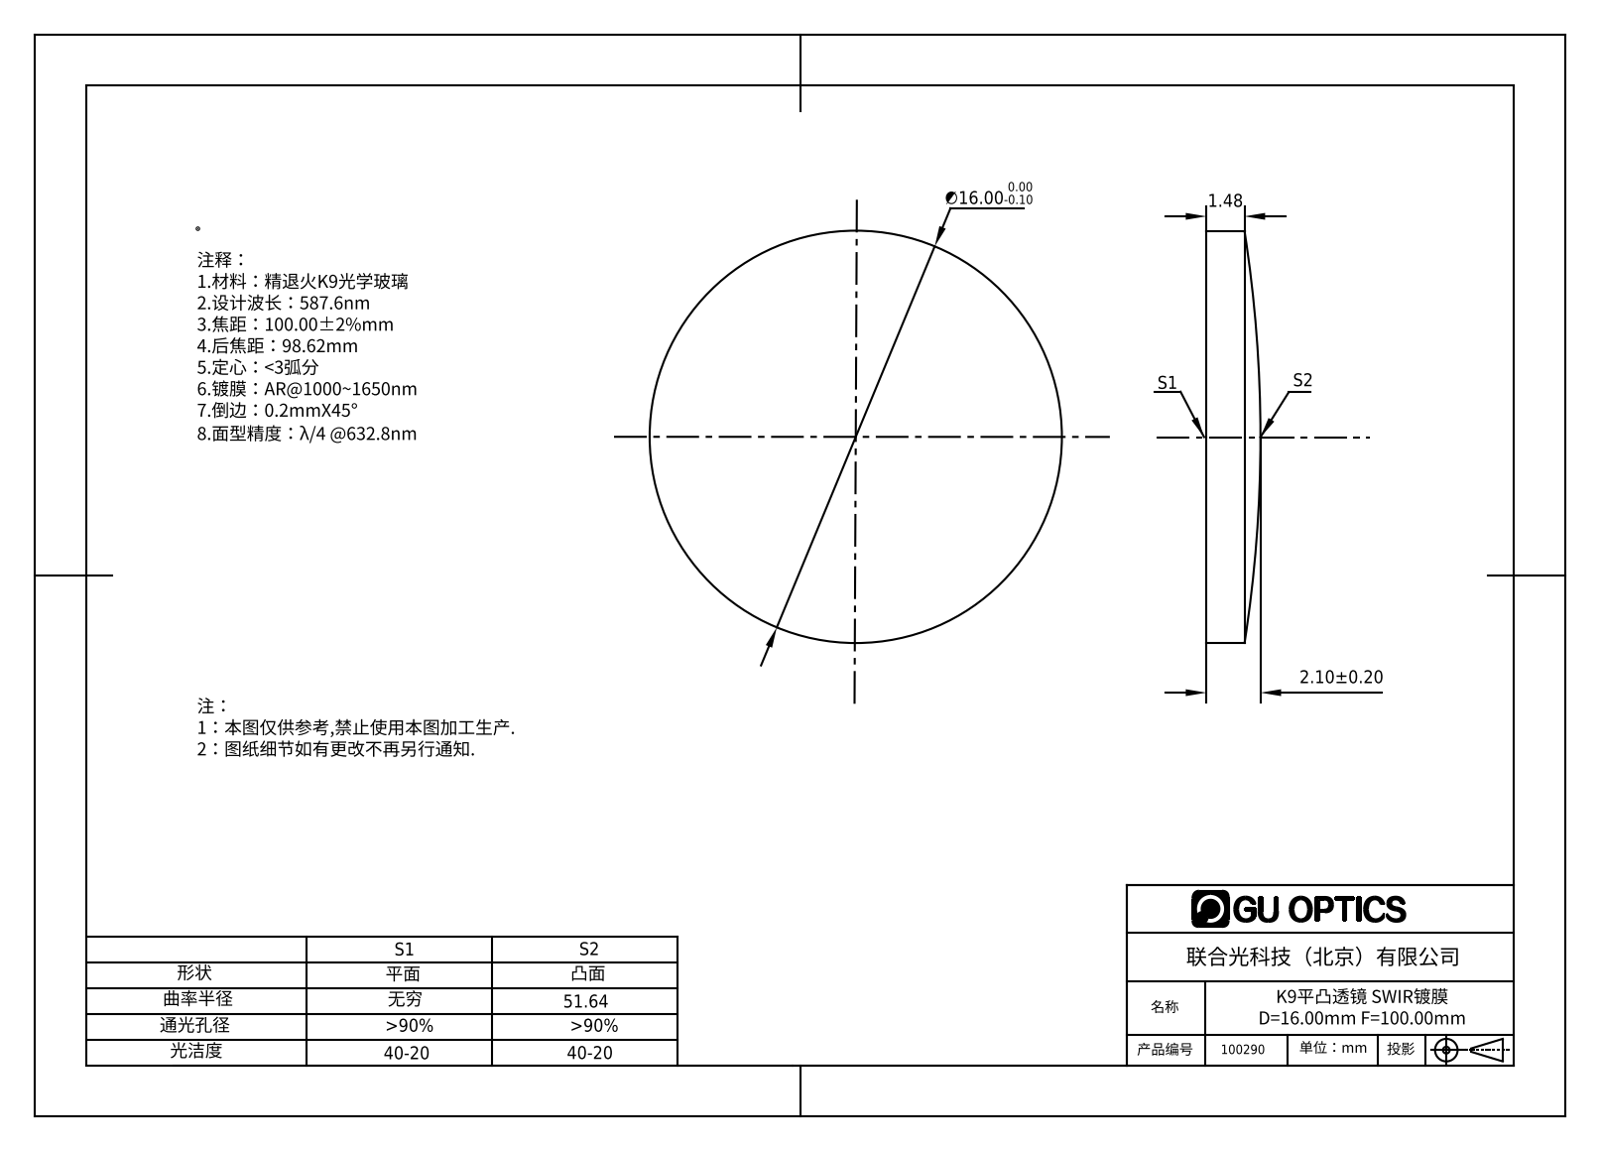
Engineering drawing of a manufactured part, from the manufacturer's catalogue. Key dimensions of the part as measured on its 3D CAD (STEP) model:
Part name (STEP PRODUCT): 100118
STEP written by: SolidWorks 2016 (AUTOMOTIVE_DESIGN)
Units: millimetres
Bodies: 1 solid, 5 faces (1 planar, 2 cylindrical, 2 other)
Overall size (bounding box): 16 × 16 × 2.1
Volume: 360 mm³ · Surface area: 478 mm²
Round bosses / shafts (diameter × count): ⌀16 ×1
